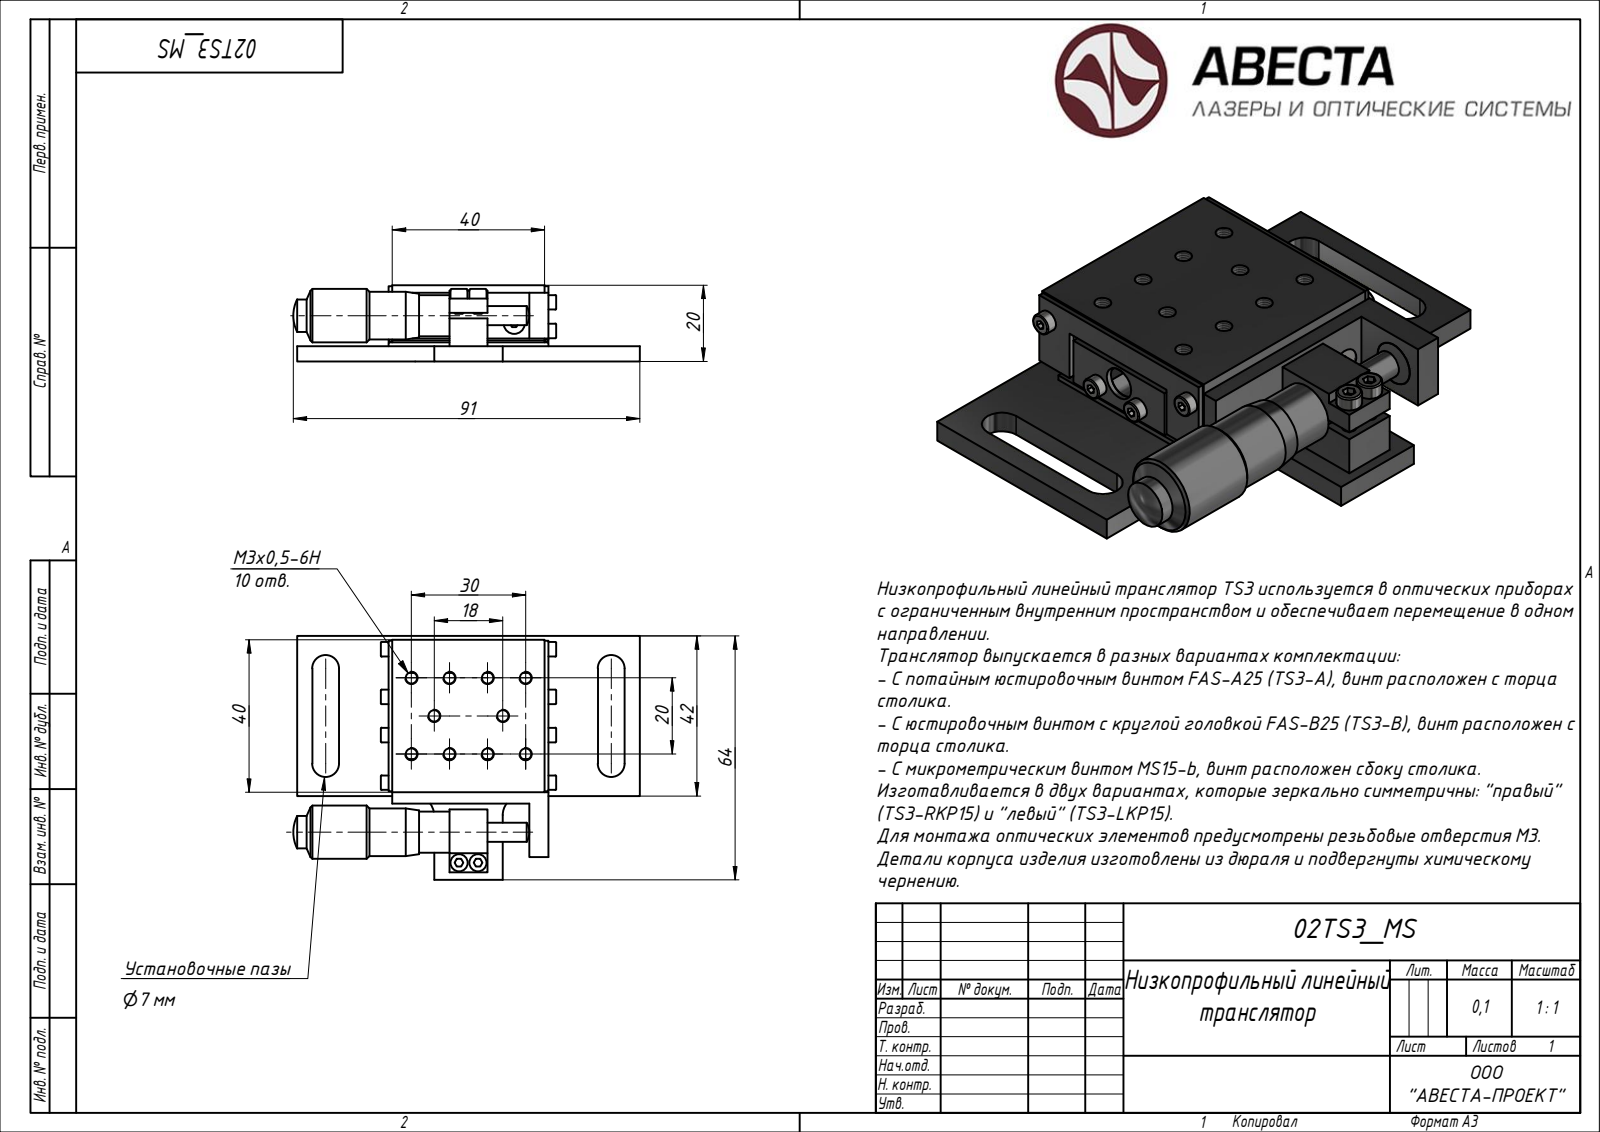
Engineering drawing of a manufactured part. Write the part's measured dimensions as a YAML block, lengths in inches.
step_written_by: "ST-DEVELOPER v15 (AUTOMOTIVE_DESIGN)"
units: inches
bodies: {solids: 16, faces: 621, planar: 0, cylindrical: 0, other: 621}
overall_size: [3.583, 2.52, 0.787]
